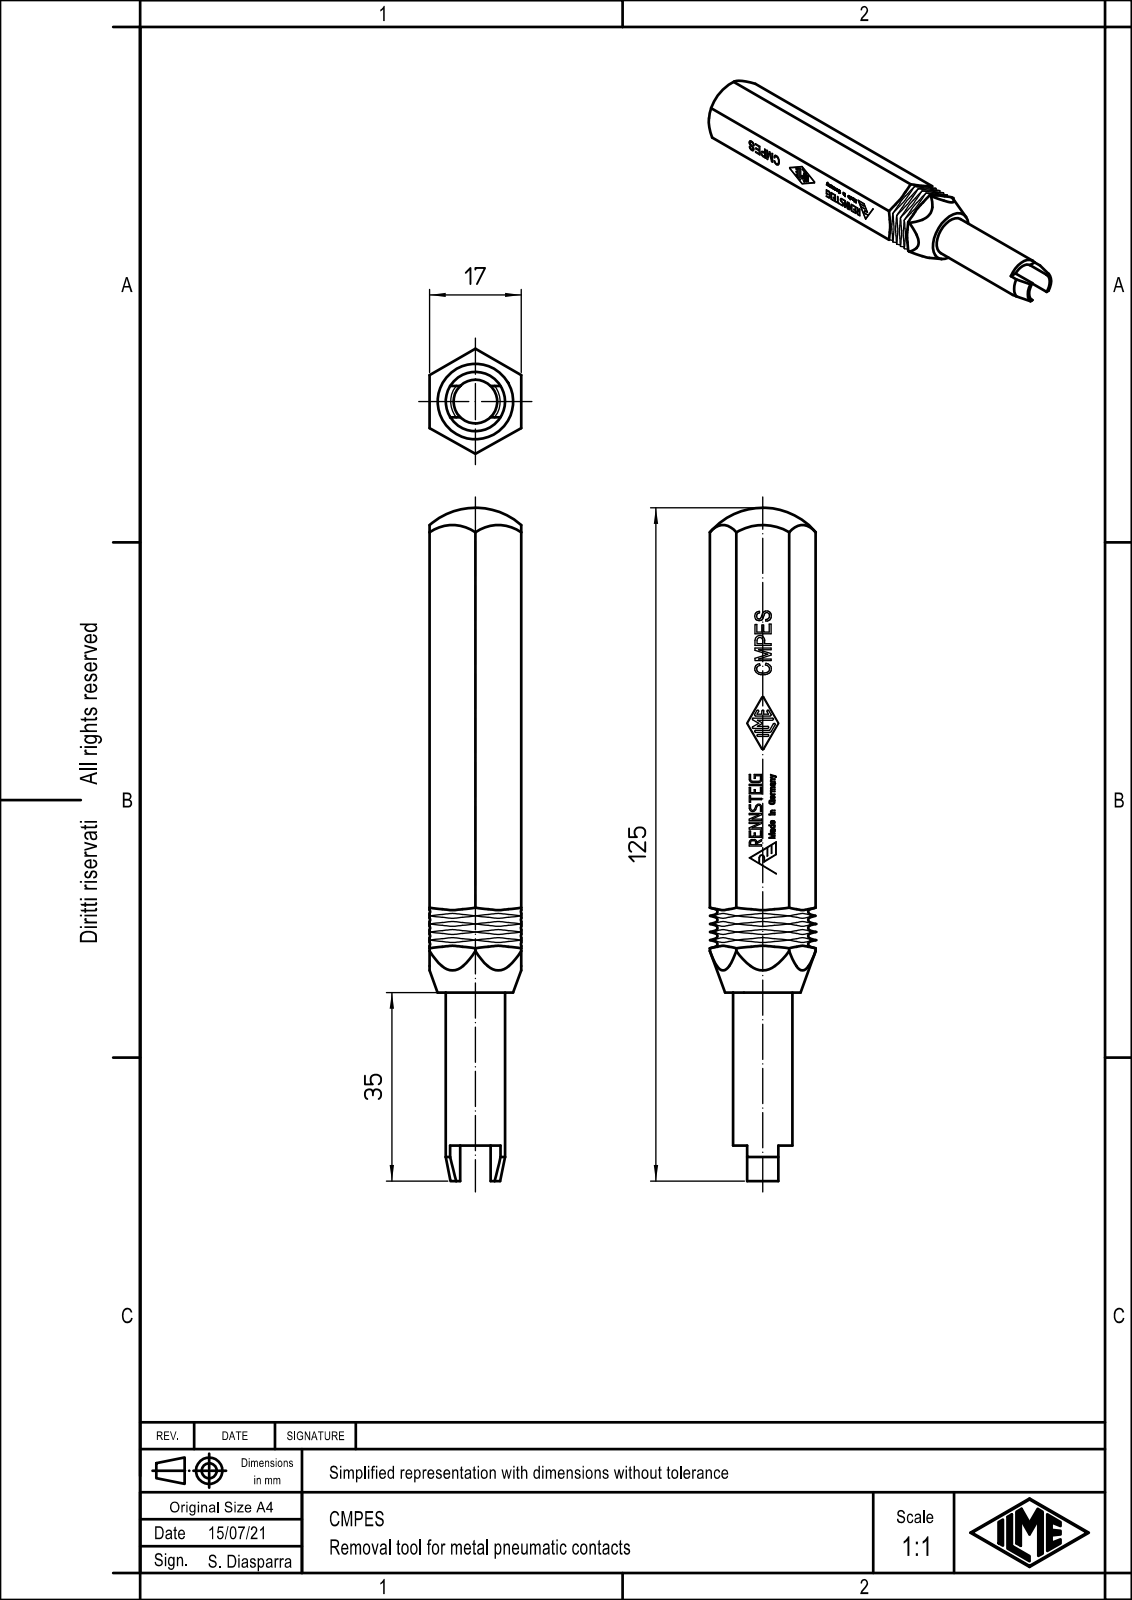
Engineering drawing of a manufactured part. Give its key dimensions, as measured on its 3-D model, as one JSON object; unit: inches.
{"part_name": "CMPES", "step_written_by": "Creo Elements/Direct Modeling 20.1B 02-Apr-2019 (C) Parametric Technology GmbH (AUTOMOTIVE_DESIGN)", "units": "inches", "bodies": {"solids": 1, "faces": 170, "planar": 88, "cylindrical": 4, "other": 78}, "overall_size": [4.921, 0.773, 0.669], "volume_in3": 1.465, "surface_area_in2": 10.9, "round_holes": [[0.319, 1]], "round_bosses_or_shafts": [[0.433, 1]], "face_to_face_distances": [0.669, 1.118, 0.228, 1.378, 0.26]}
